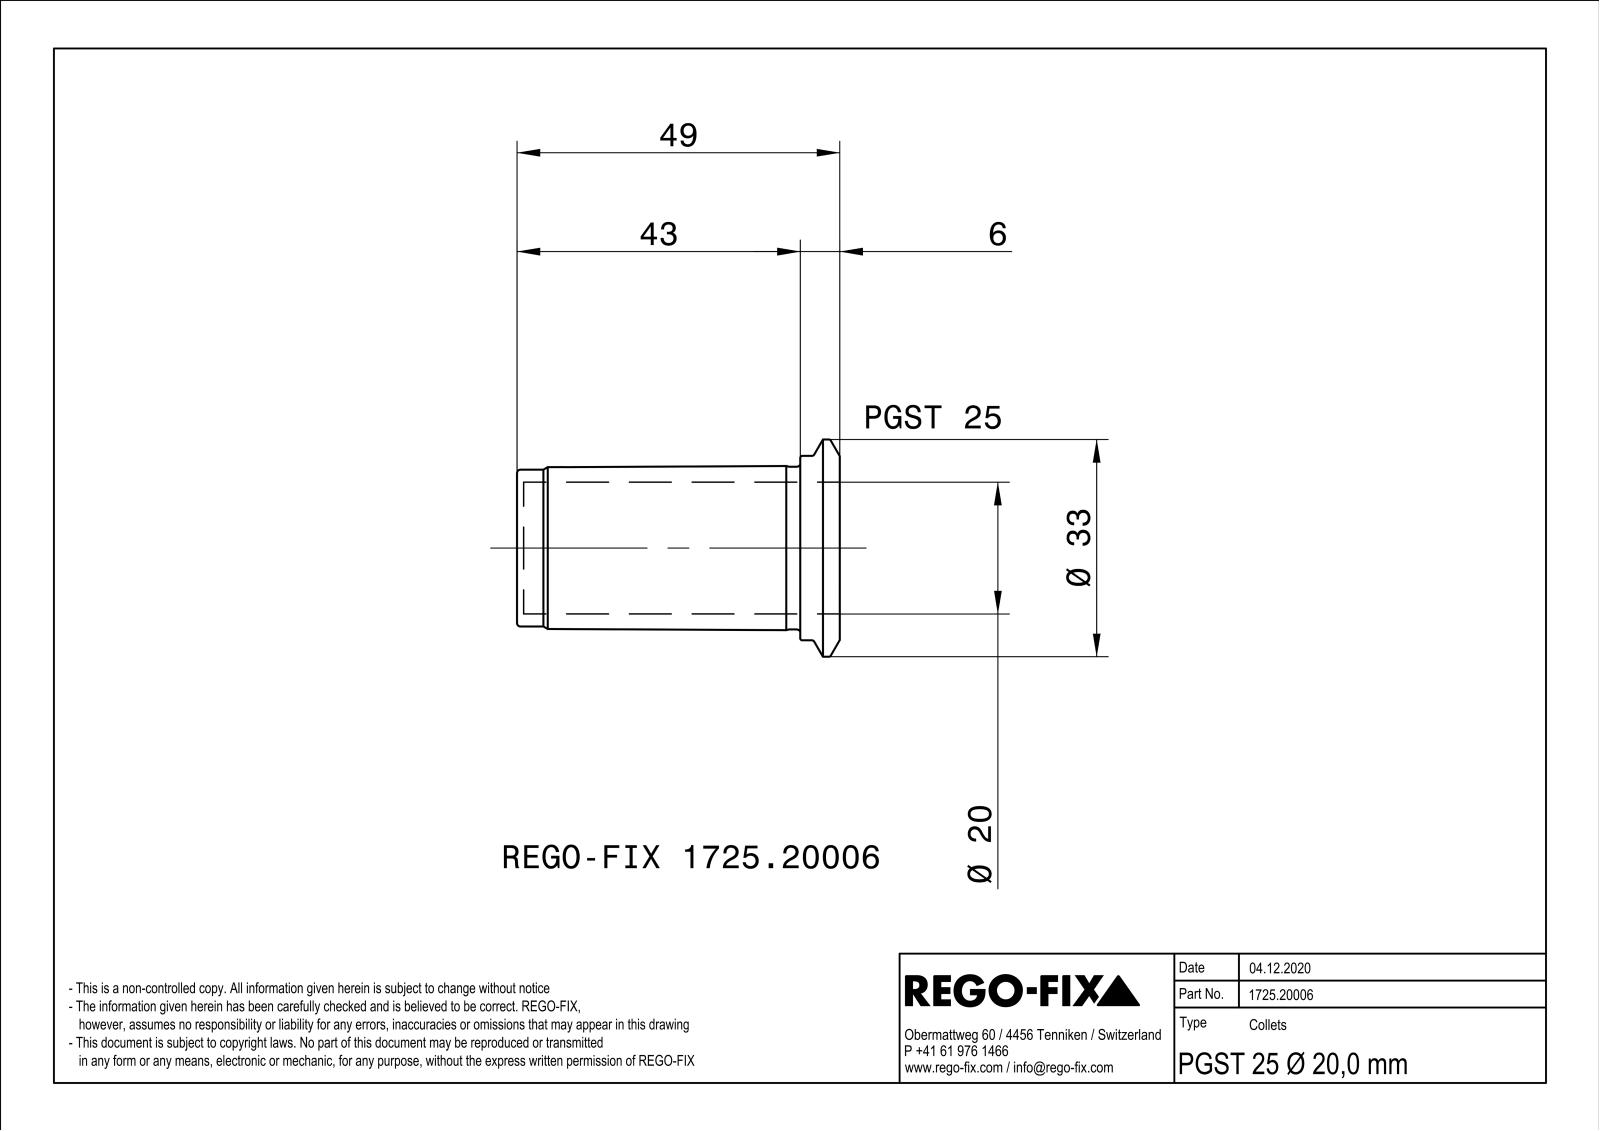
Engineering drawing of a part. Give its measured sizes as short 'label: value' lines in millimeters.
name: NOCUT
written by: SIEMENS PLM Software Solid Edge ST10 (AUTOMOTIVE_DESIGN)
unit: mm
bodies: 2 solids, 42 faces (7 planar, 14 cylindrical, 21 other)
size: 49 × 32.98 × 32.98
volume: 9 590 mm³; area: 8 976 mm²
holes: 3× ⌀3, 1× ⌀12, 1× ⌀20, 1× ⌀20.2, 1× ⌀21.19, 1× ⌀22.3
bosses: 1× ⌀32.98, 1× ⌀28, 1× ⌀24.7, 1× ⌀23.8, 1× ⌀22, 1× ⌀21
face distances: 49, 48, 1, 43.5, 4.5, 5.5, 6, 37.5, 42, 43
hole spacings: 8.5, 14.72
